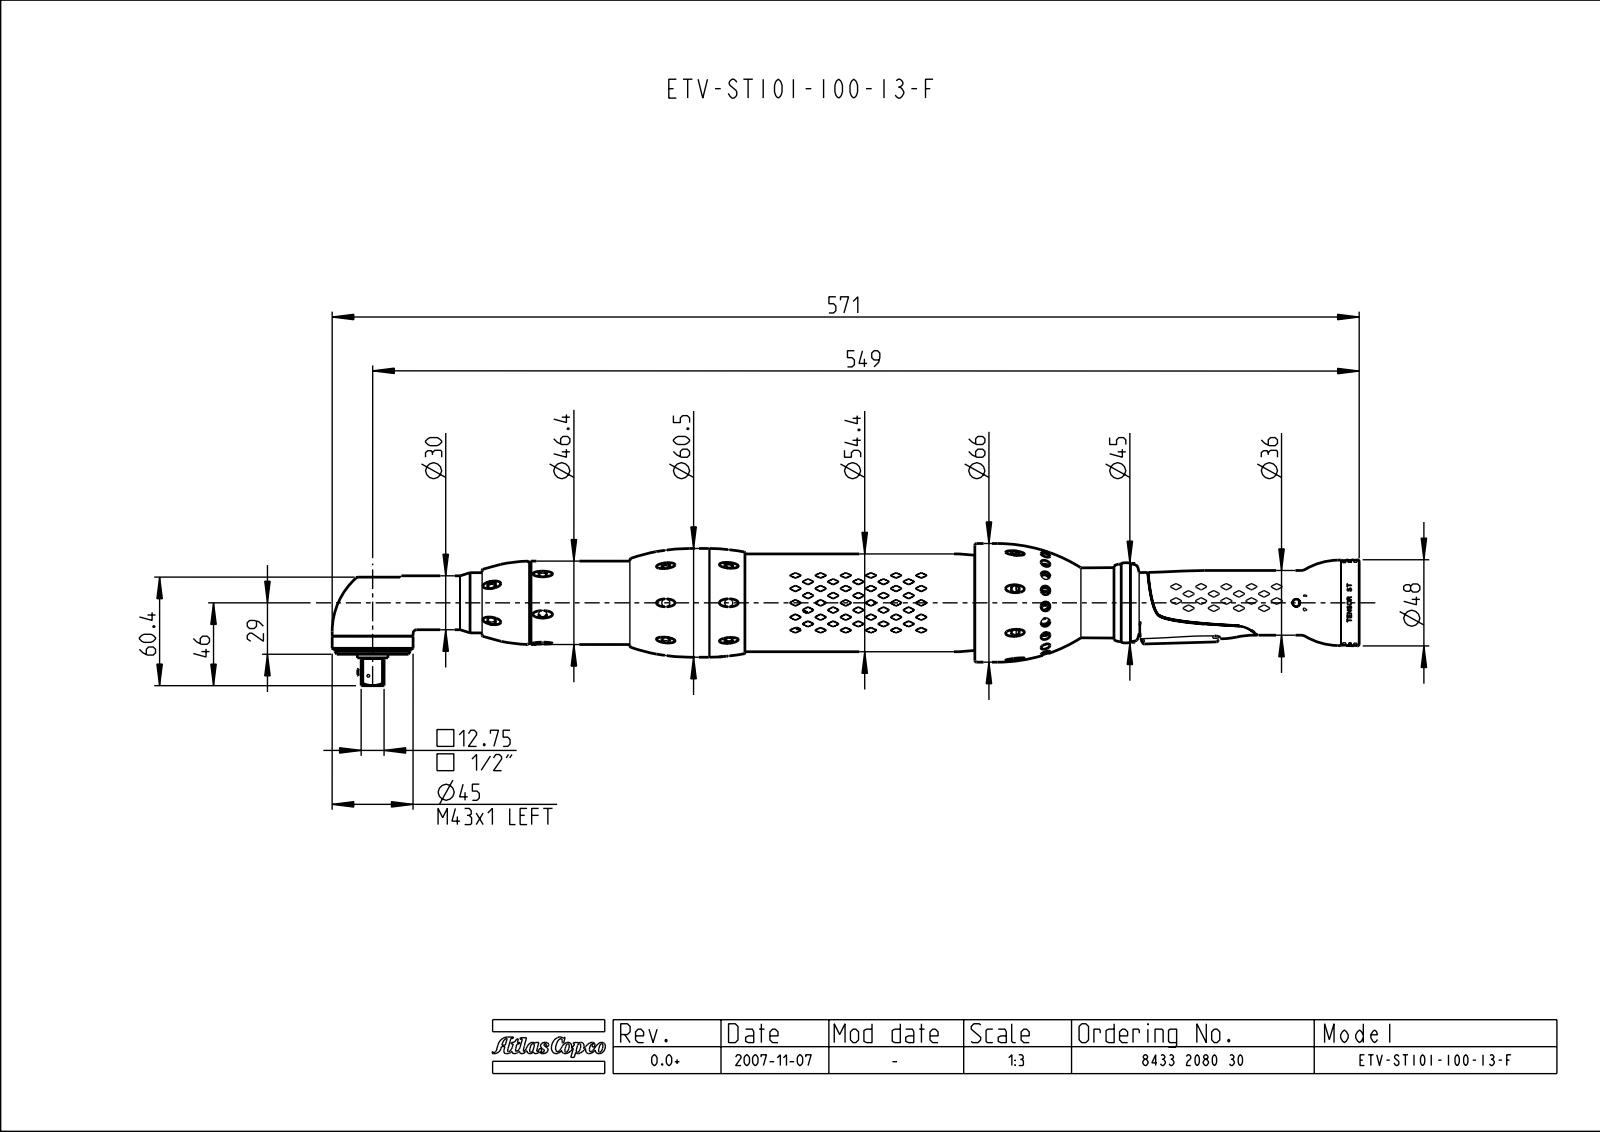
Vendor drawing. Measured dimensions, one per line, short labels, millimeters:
name: ETV-ST101-100-13-F_SW
written by: PRO/ENGINEER BY PARAMETRIC TECHNOLOGY CORPORATION, 2007090 (CONFIG_CONTROL_DESIGN)
unit: mm
bodies: 0 solids, 769 faces (83 planar, 319 cylindrical, 367 other)
size: 571.31 × 79.11 × 66
holes: 19× ⌀4.5, 19× ⌀5, 1× ⌀36.4, 1× ⌀39, 1× ⌀61.92
bosses: 2× ⌀45, 1× ⌀66, 1× ⌀60.5, 1× ⌀54.4, 1× ⌀52.6, 1× ⌀50.8, 1× ⌀46.4, 1× ⌀43
rounds: 11× R2, 6× R1.5, 5× R34.5, 4× R35.5, 3× R0.45, 3× R2.25, 1× R0.5, 1× R2.5
face distances: 10.5, 5.96, 16.46, 148.64, 154.6, 165.1, 26, 15.5, 180.6, 31.96
hole spacings: 0.5, 35, 16.8, 16.3, 34.98, 35.02
